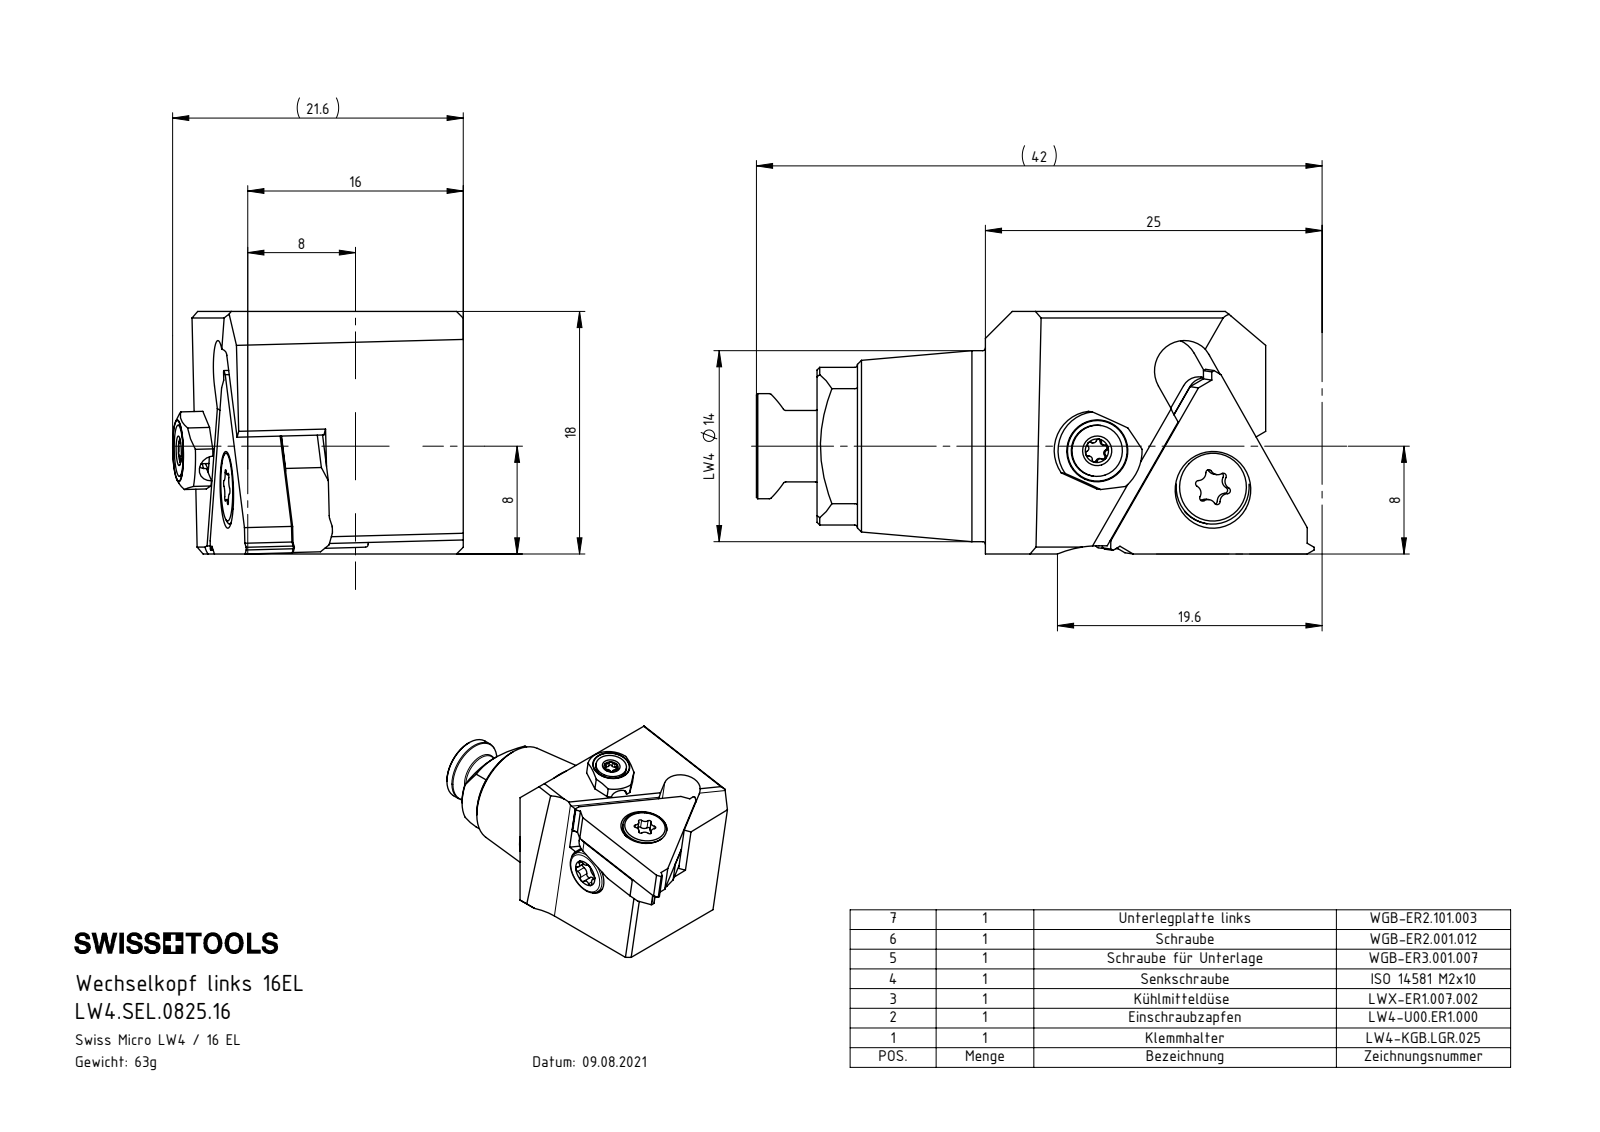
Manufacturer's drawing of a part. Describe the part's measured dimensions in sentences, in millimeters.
The part is named "ISO 14581 - M2x10; WGB-ER2.101.003_A; LW4.SEL.0825.16; LW4-U00.ER1.000_B (+5 more)". Its 3-D file was written by "SolidWorks 2022 (CONFIG_CONTROL_DESIGN)". It is 8 solids with 314 faces: 106 planar, 111 cylindrical and 97 other. Overall it measures 41.41 by 21.58 by 18 millimeters. Its volume is 7 629 cubic millimeters and its surface area 4 673 square millimeters. Round holes: 2 of diameter 2.58, 2 of diameter 3, 1 of diameter 1.6, 1 of diameter 2, 1 of diameter 2.5, 1 of diameter 3.9, 1 of diameter 4, 1 of diameter 5.5. Round bosses or shafts: 2 of diameter 5.5, 1 of diameter 14.17, 1 of diameter 7.7, 1 of diameter 6, 1 of diameter 5.3, 1 of diameter 5, 1 of diameter 3.8, 1 of diameter 3.18. Partial cylindrical surfaces (rounded edges, fillets, slot ends): 8 of radius 0.2, 6 of radius 0.23, 6 of radius 0.24, 6 of radius 0.34, 6 of radius 0.57, 6 of radius 0.57, 2 of radius 2.9, 1 of radius 0.5. The main face-to-face distances are 6.85, 3.66, 3.65, 3.2, 6.86, 3.19, 6.84, 18, 0.59, 7.5. The hole center spacings are 9.5, 9.53, 9.55, 9.56, 9.58, 9.59.
